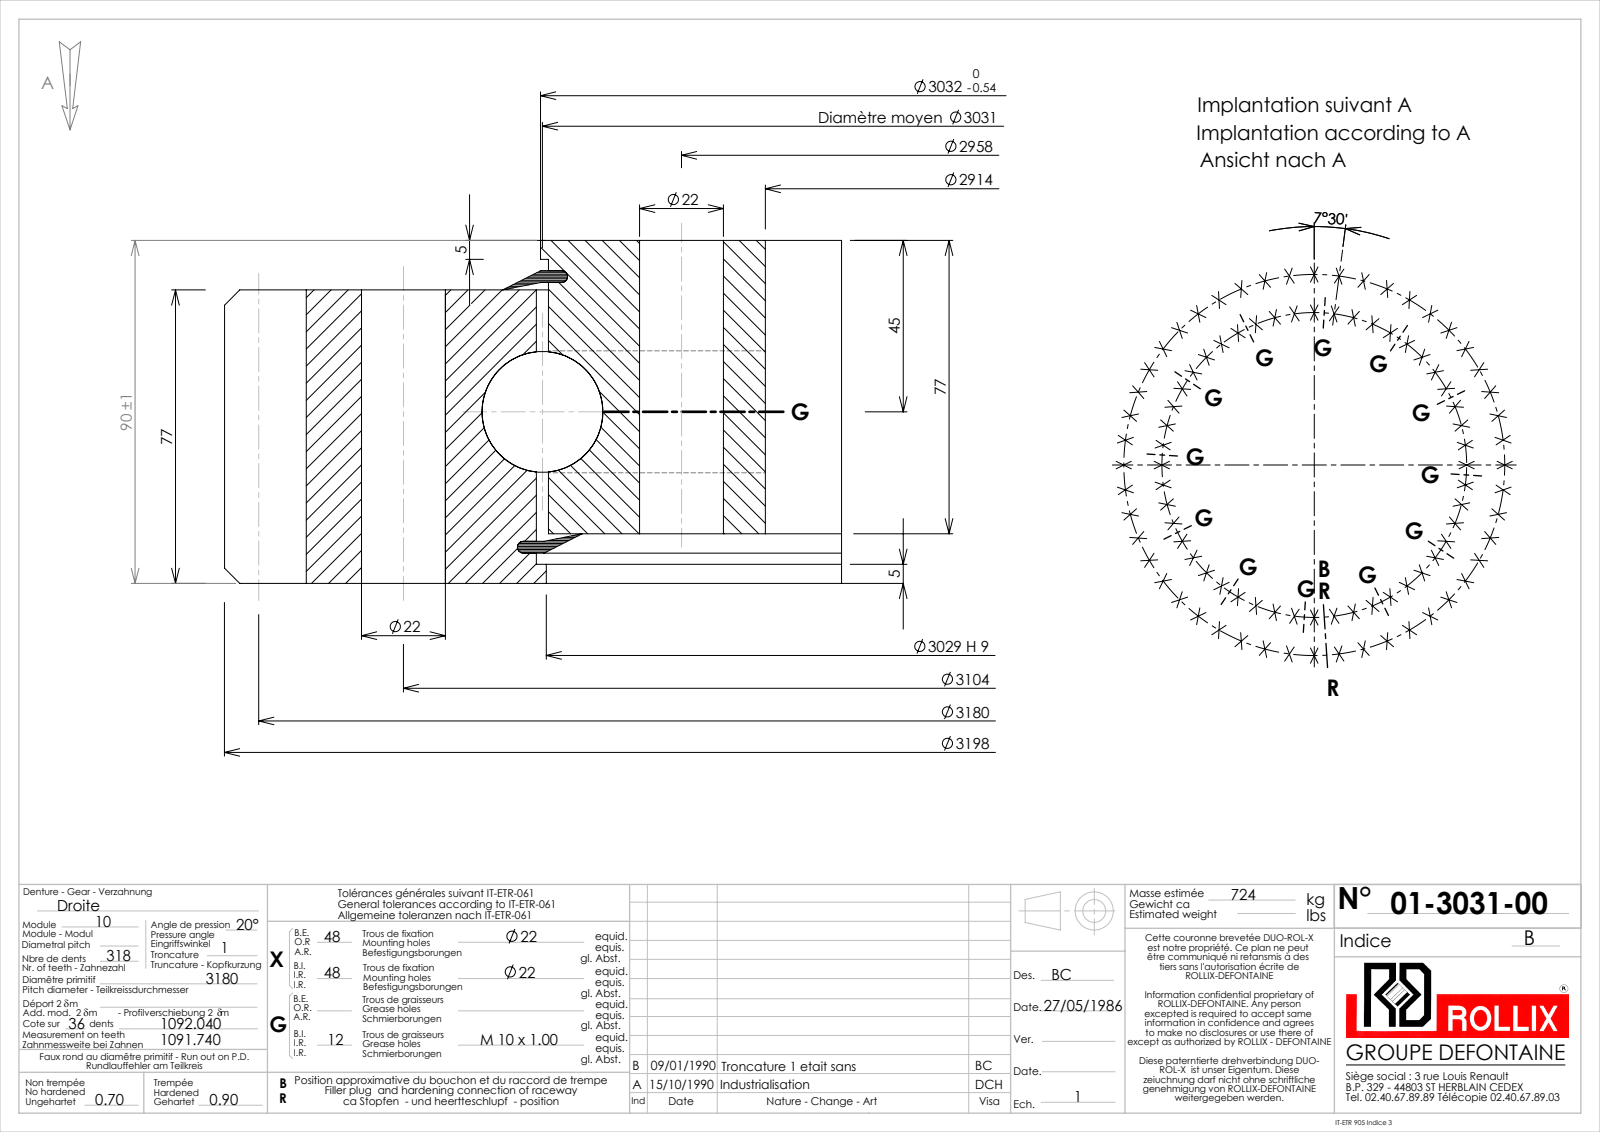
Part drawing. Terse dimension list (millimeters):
name: 01-3031-00
written by: SolidWorks 2016 (CONFIG_CONTROL_DESIGN)
unit: mm
bodies: 5 solids, 2185 faces (650 planar, 871 cylindrical, 664 other)
size: 3198 × 3197.92 × 90
volume: 86 220 000 mm³; area: 7 830 000 mm²
holes: 96× ⌀22, 12× ⌀9, 1× ⌀2914, 1× ⌀3029, 1× ⌀3034.18
bosses: 1× ⌀3032, 1× ⌀3027.82
rounds: 1× R1577.5, 1× R1599
face distances: 77, 13, 90, 64, 11.05, 78.95, 1.95, 65.95, 7.95, 82.05
hole spacings: 1552, 203.01, 803.37, 1724.49, 605.56, 2194.86, 997.75, 2333.71
